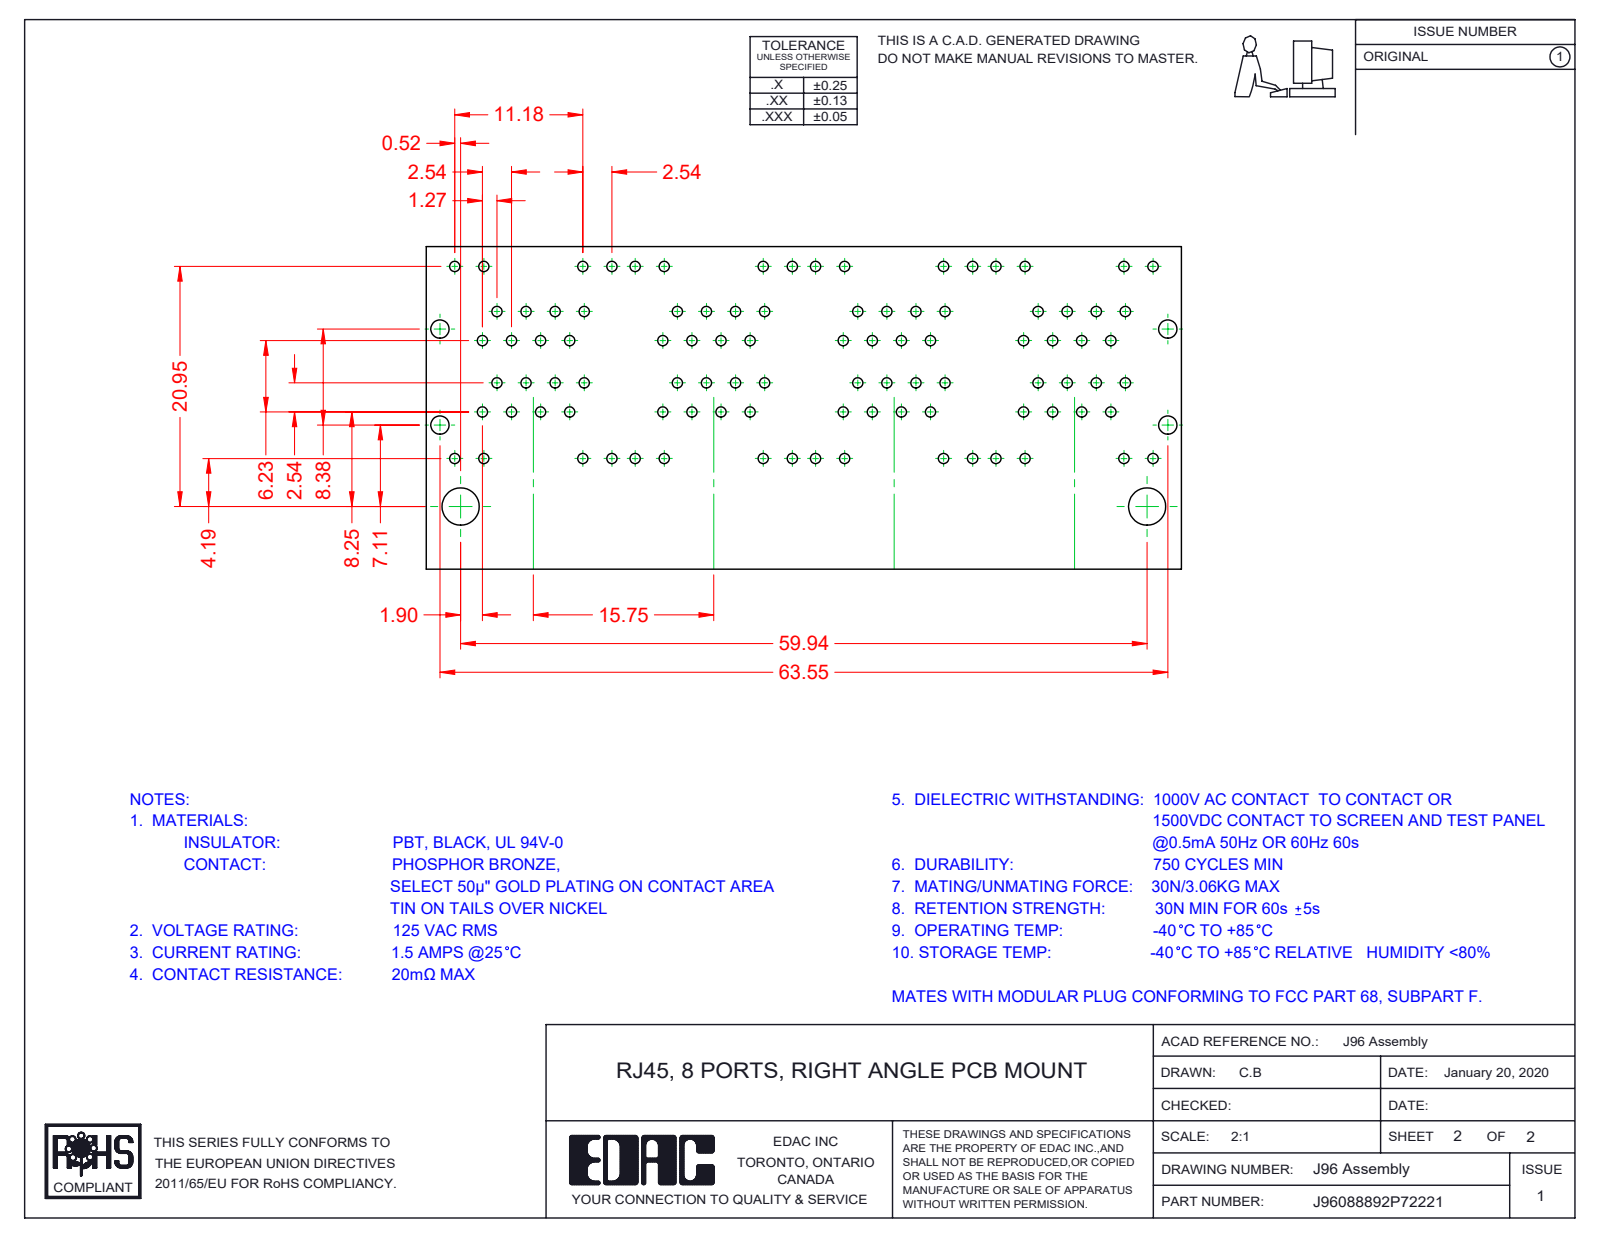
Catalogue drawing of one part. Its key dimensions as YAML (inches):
part_name: "96 Contacts Upper; 96 LED RH Lower_2-Red; 96 Shield_8 Ports LED - EMI; 96 Insulator Insert (+8 more)"
step_written_by: "SolidWorks 2016 (CONFIG_CONTROL_DESIGN)"
units: inches
bodies: {solids: 96, faces: 7820, planar: 6105, cylindrical: 1404, other: 311}
overall_size: [2.652, 1.235, 1.129]
volume: 1.474
surface_area: 98.57
round_holes:
  - {diameter: 0.067, count: 3}
round_bosses_or_shafts:
  - {diameter: 0.066, count: 3}
partial_cylinders:
  - {radius: 0.01, count: 124}
  - {radius: 0.014, count: 73}
  - {radius: 0.039, count: 72}
  - {radius: 0.02, count: 49}
  - {radius: 0.036, count: 32}
  - {radius: 0.008, count: 27}
  - {radius: 0.011, count: 14}
  - {radius: 0.028, count: 11}
face_to_face_distances: [0.62, 0.014, 0.392, 0.046, 0.063, 0.021, 0.393, 0.401, 0.499, 0.133]
hole_center_spacings: [0.62, 1.24]
